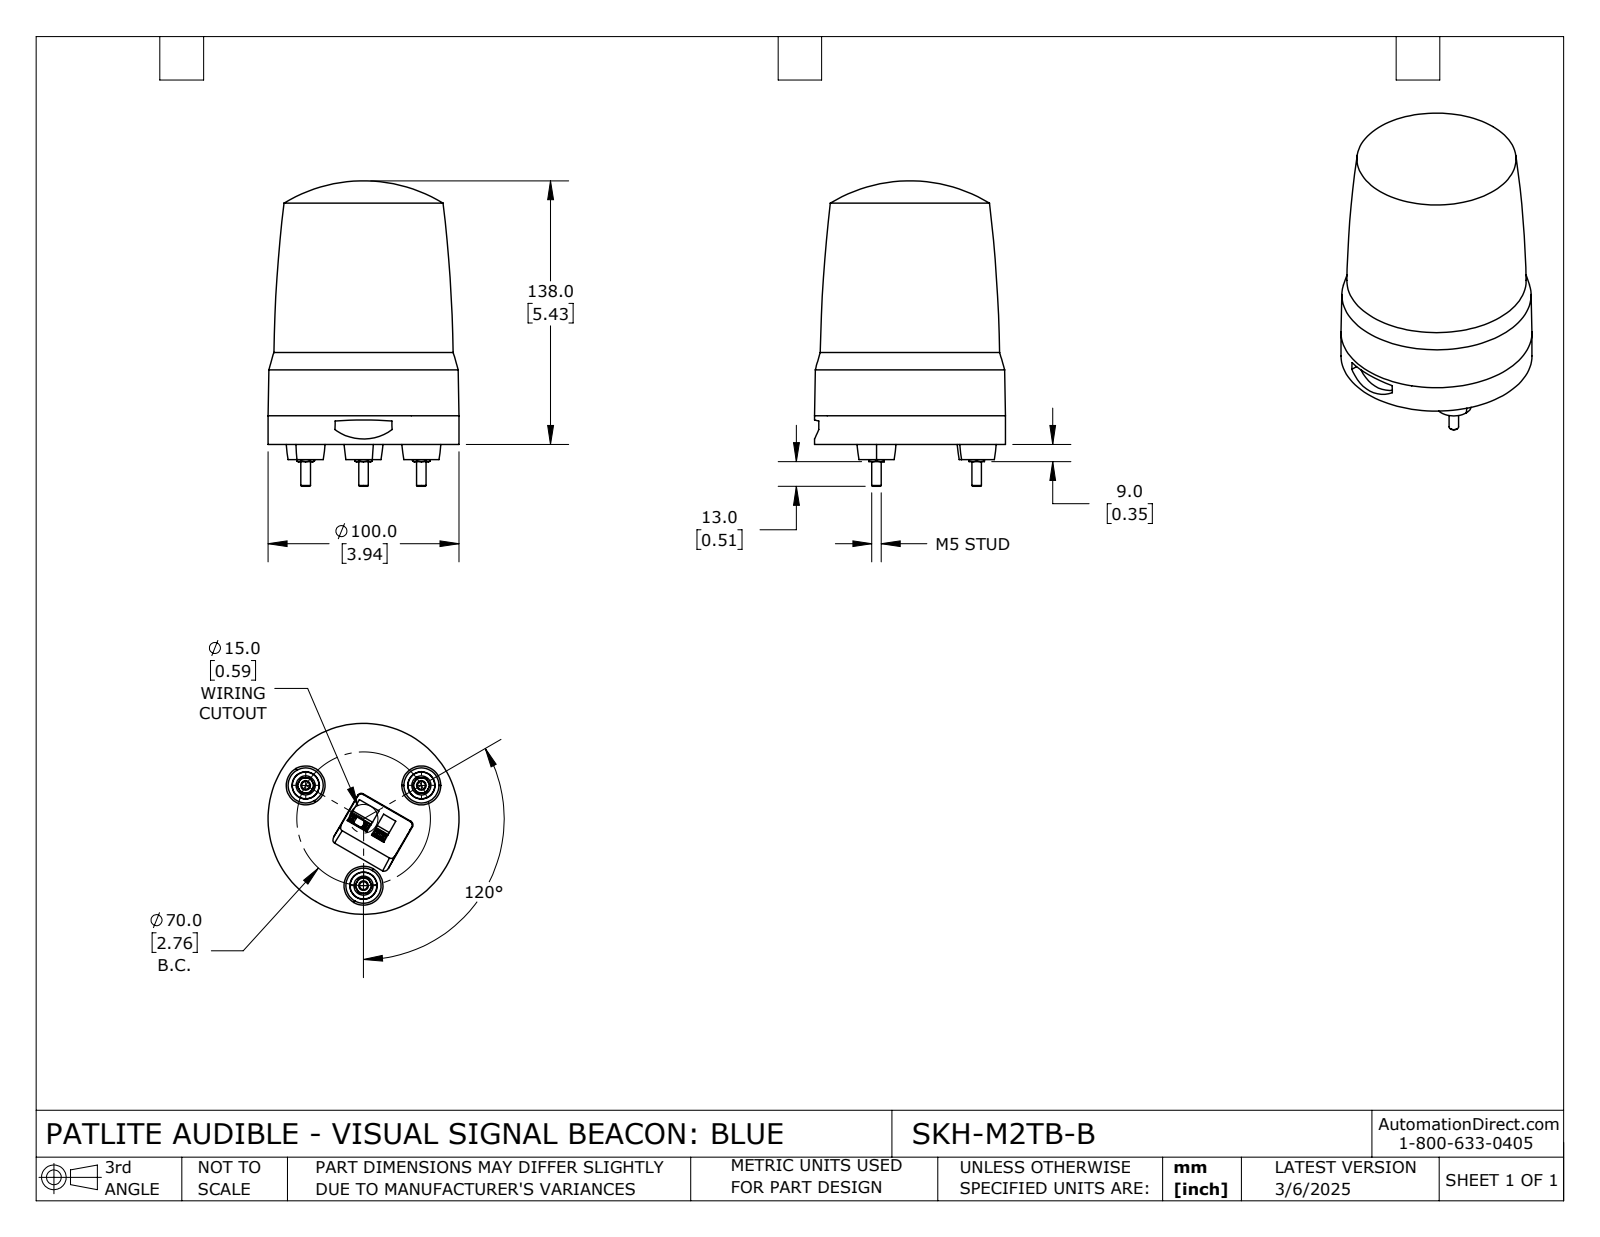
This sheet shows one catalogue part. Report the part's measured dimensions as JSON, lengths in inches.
{"part_name": "SKH-M2TB-B", "step_written_by": "SolidWorks 2024 (CONFIG_CONTROL_DESIGN)", "units": "inches", "bodies": {"solids": 1, "faces": 270, "planar": 146, "cylindrical": 25, "other": 99}, "overall_size": [6.299, 3.937, 3.937], "volume_in3": 54.66, "surface_area_in2": 89.33, "round_bosses_or_shafts": [[0.394, 3], [0.197, 3], [3.937, 1]], "partial_cylinders_radius": [[0.079, 4], [0.012, 2], [0.199, 2], [1.772, 1], [3.154, 1]], "face_to_face_distances": [0.742, 0.315, 0.866, 1.057, 0.118, 0.15, 0.165, 0.907, 0.234, 0.583]}
